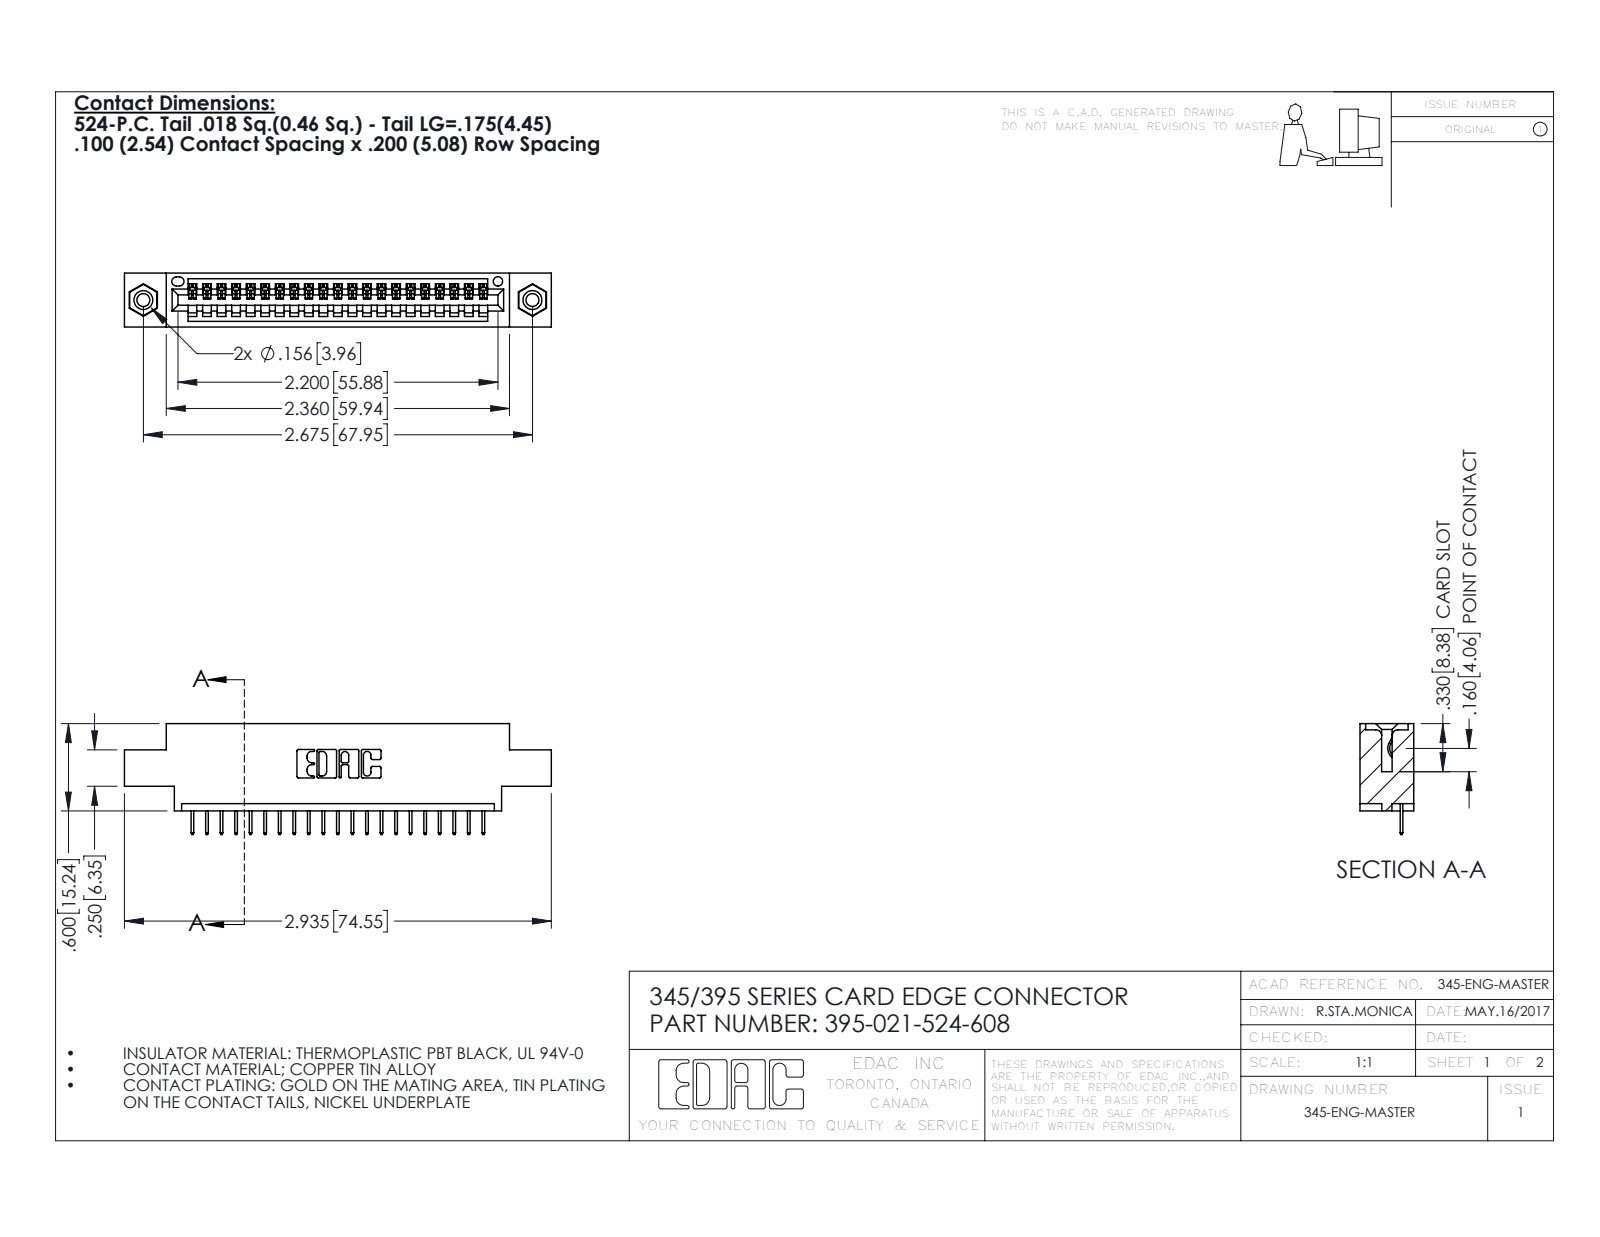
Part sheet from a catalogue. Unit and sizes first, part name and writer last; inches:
Units: inches
Overall size (bounding box): 2.935 × 0.762 × 0.37
Round holes (diameter × count): ⌀0.089 ×2, ⌀0.125 ×2, ⌀0.156 ×2, ⌀0.064 ×1
Round bosses / shafts (diameter × count): ⌀0.155 ×2
Partial cylindrical surfaces — rounded edges, fillets, slot ends (radius × count): R0.006 ×42, R0.01 ×22, R0.007 ×6, R0.031 ×6, R0.026 ×3, R0.031 ×2, R0.04 ×2, R0.014 ×1
Main face-to-face distances: 0.072, 0.298, 0.37, 0.2, 0.098, 0.272, 0.025, 0.225, 0.072, 0.175
Hole centre spacings: 0.27, 2.441, 2.675
Volume: 0.409 in³ · Surface area: 13.19 in²
Bodies: 24 solids, 1492 faces (1082 planar, 394 cylindrical, 16 other)
Part name (STEP PRODUCT): 345-250-001_345-250-003-102; 345 Part_0.170 Offset - 0.156 Dia-TI; 345-292-001_345-293-124; 395-021-524-608
STEP written by: SolidWorks 2016 (CONFIG_CONTROL_DESIGN)
